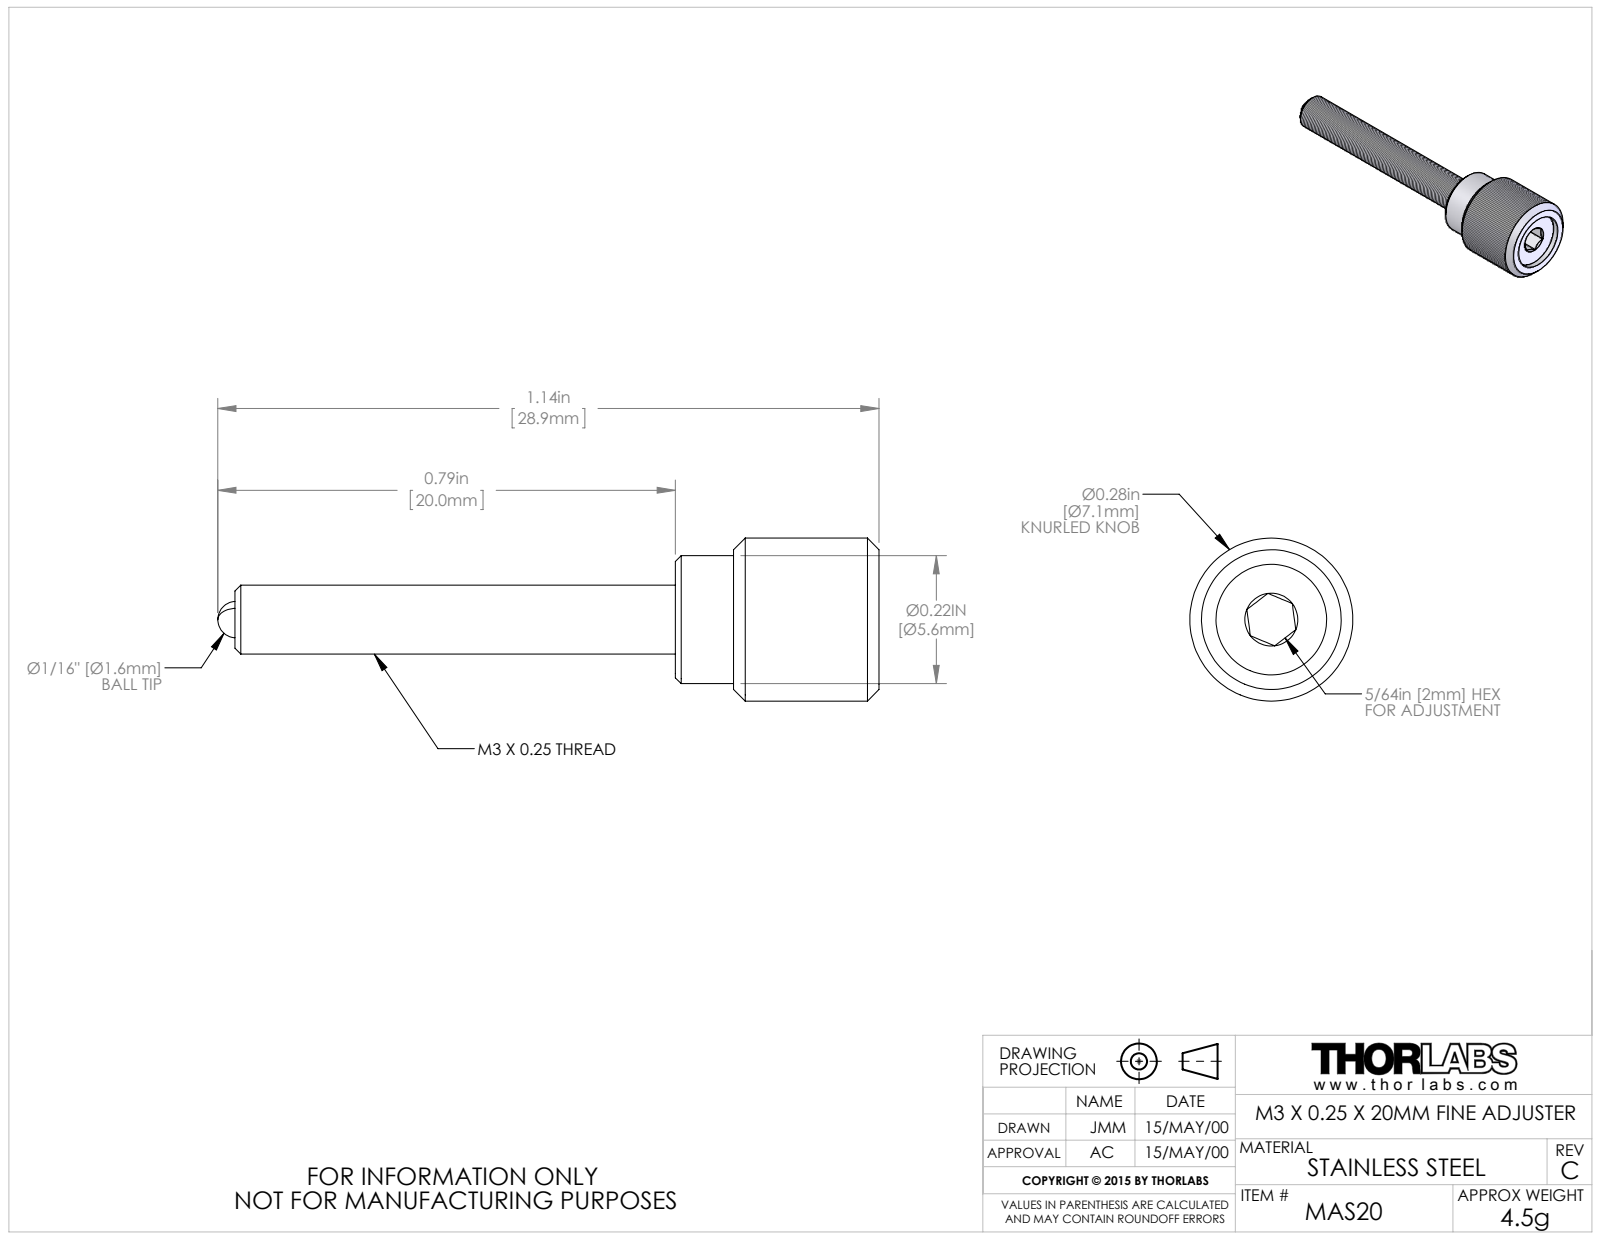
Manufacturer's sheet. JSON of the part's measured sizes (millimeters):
{"part_name": "5123-E0W", "step_written_by": "SolidWorks 2011 (AUTOMOTIVE_DESIGN)", "units": "millimeters", "bodies": {"solids": 3, "faces": 50, "planar": 14, "cylindrical": 12, "other": 24}, "overall_size": [27.8, 7.1, 7.1], "volume_mm3": 430, "surface_area_mm2": 561, "round_holes": [[1.6, 1], [3, 1], [4.8, 1]], "round_bosses_or_shafts": [[7.1, 1], [5.6, 1]], "face_to_face_distances": [3.3, 2.5, 3.8, 0.5, 5.1, 8.4, 8.9, 2, 5.8, 6.4]}
